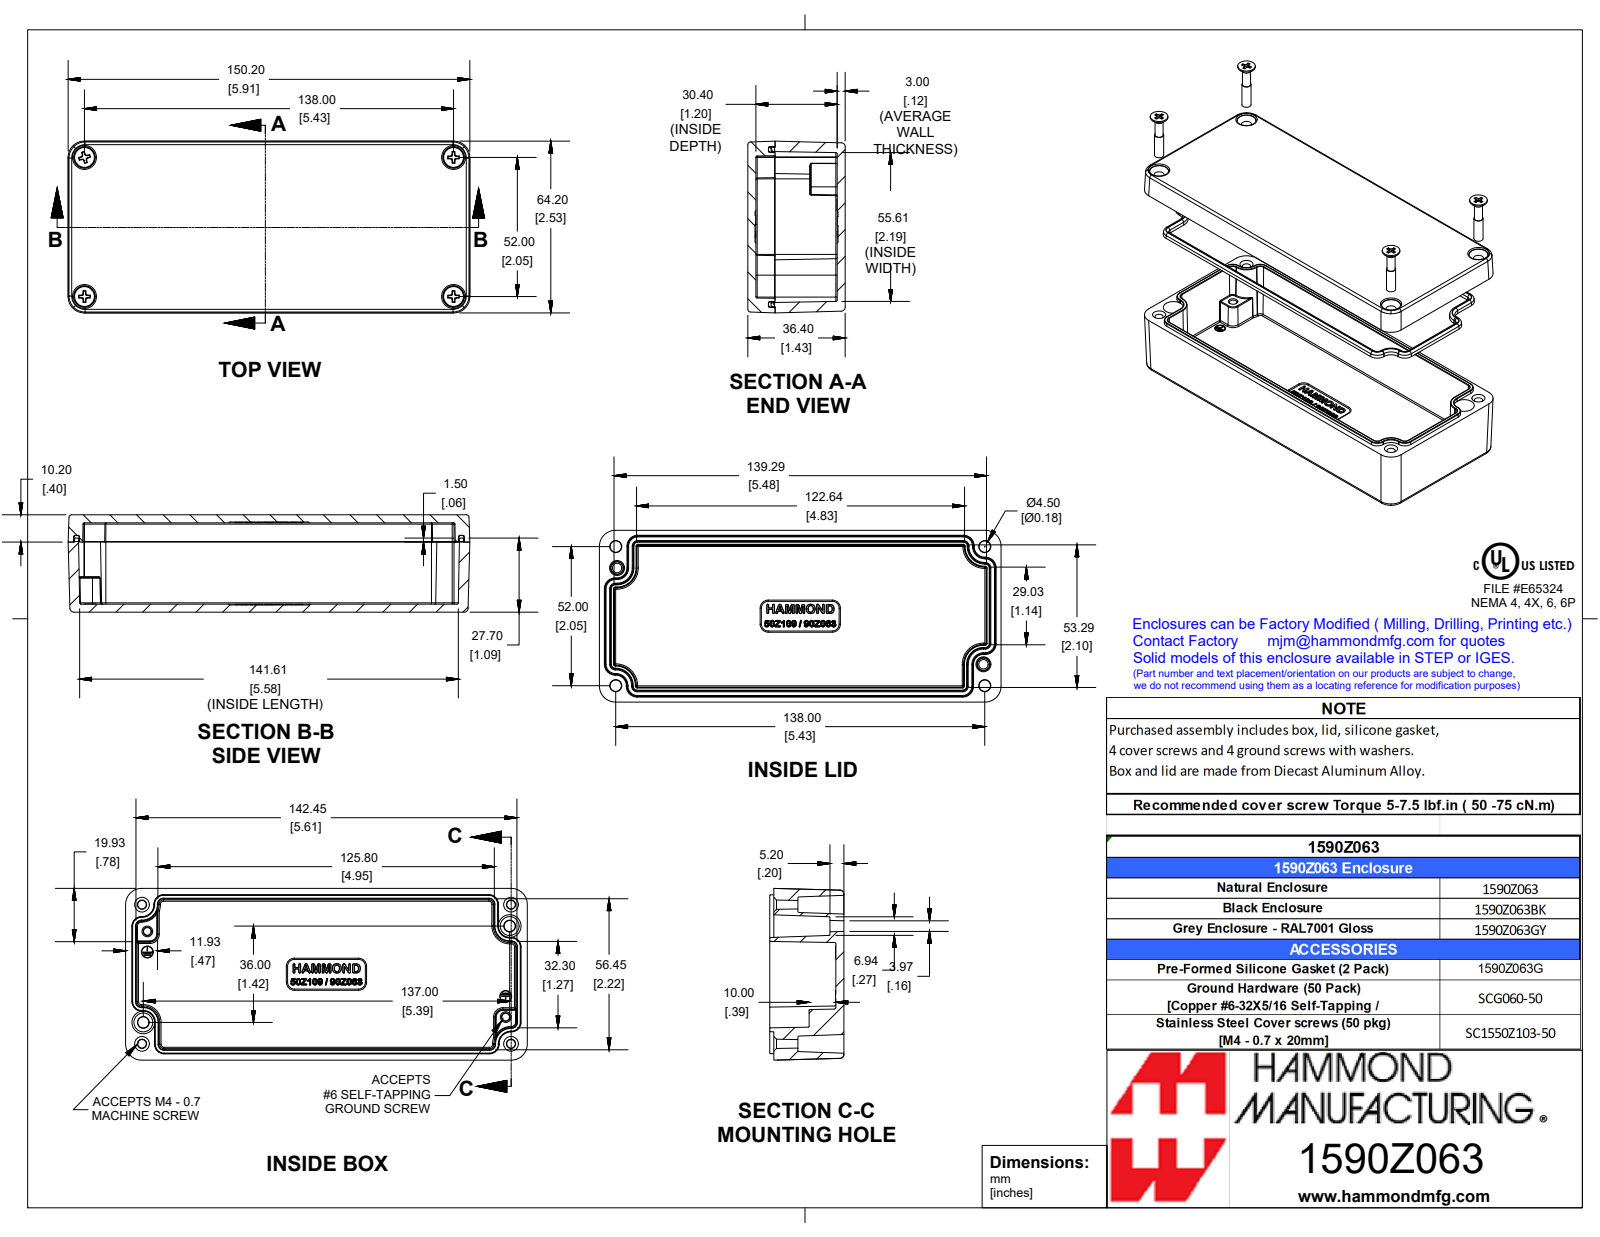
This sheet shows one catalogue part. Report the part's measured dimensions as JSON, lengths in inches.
{"part_name": "1590Z063", "step_written_by": "SolidWorks 2019 (CONFIG_CONTROL_DESIGN)", "units": "inches", "bodies": {"solids": 7, "faces": 1391, "planar": 413, "cylindrical": 176, "other": 802}, "overall_size": [5.913, 2.528, 1.433], "volume_in3": 7.042, "surface_area_in2": 115.8, "round_bosses_or_shafts": [[0.15, 4], [0.135, 4]], "partial_cylinders_radius": [[0.008, 60], [0.012, 34], [0.02, 34], [0.039, 28], [0.236, 8], [0.059, 4]], "face_to_face_distances": [0.118, 1.315, 1.433, 1.197, 0.283, 1.031, 0.913, 0.402, 2.159, 0.394]}
